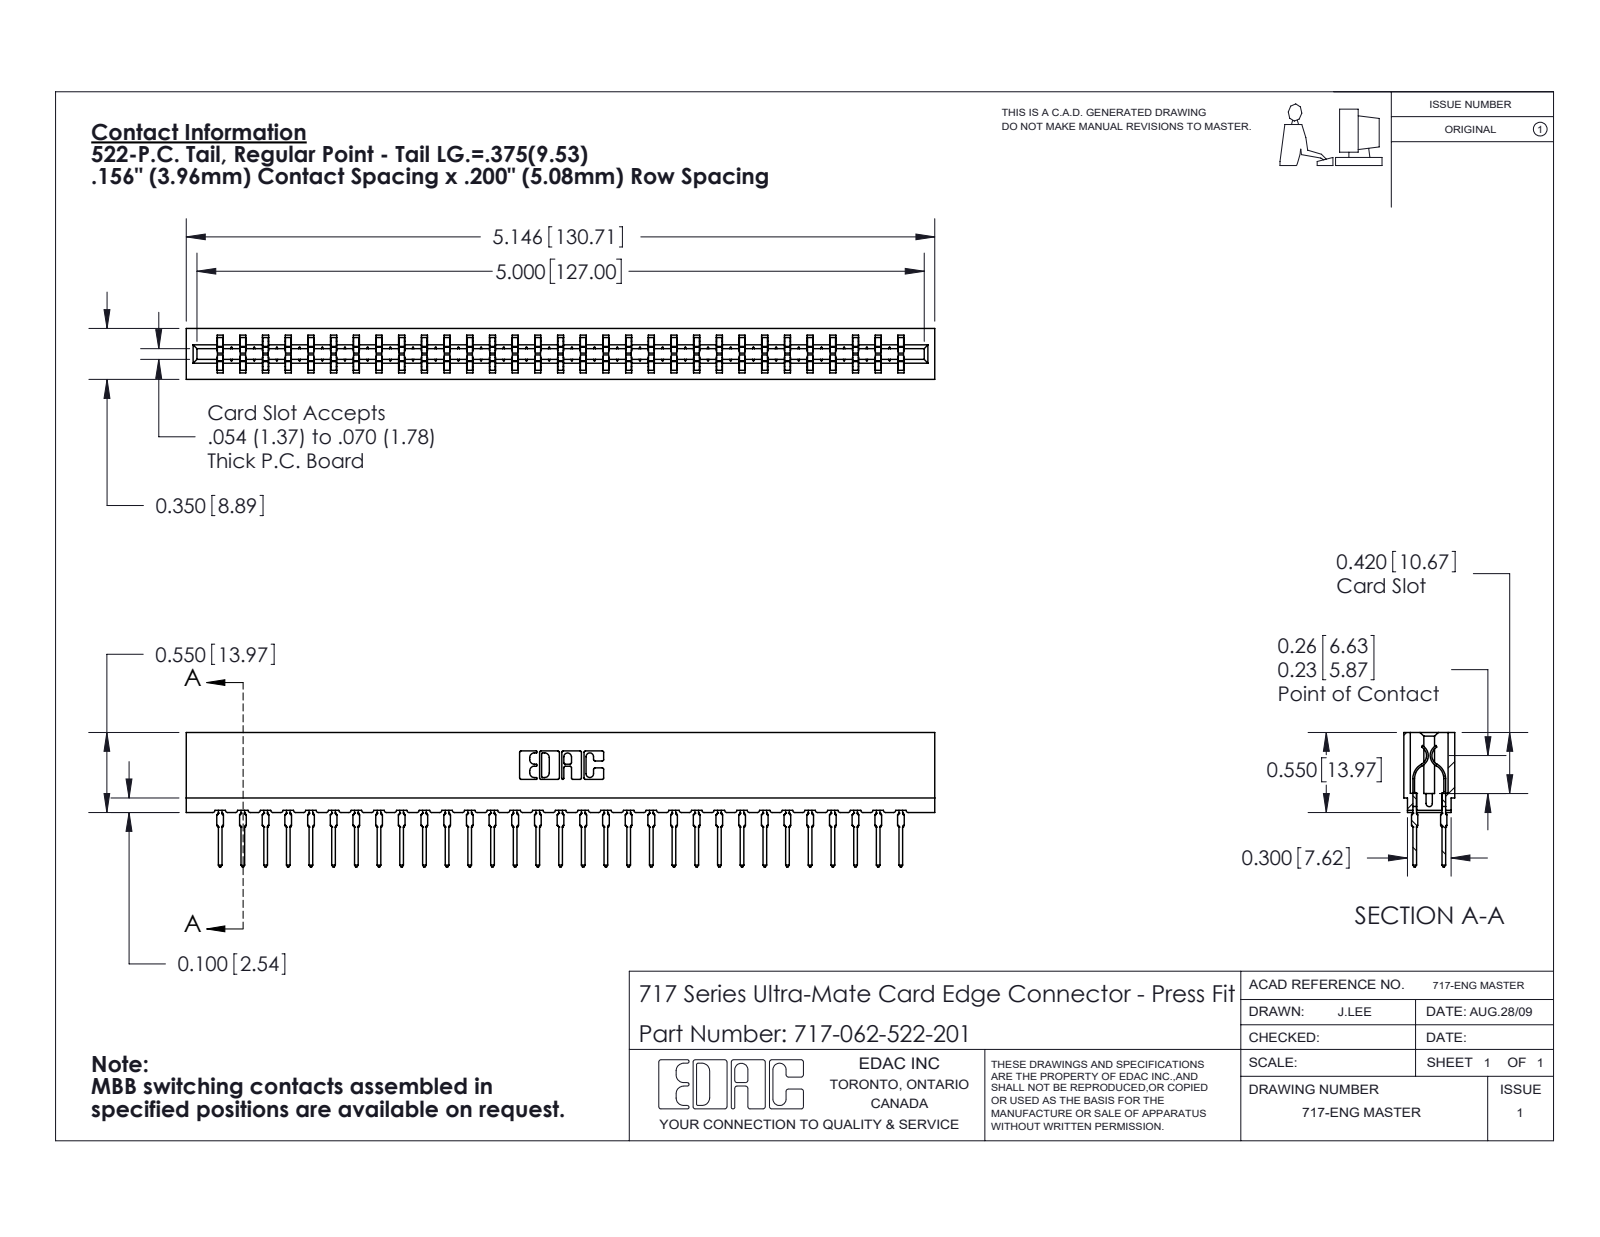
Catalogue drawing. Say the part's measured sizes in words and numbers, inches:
The part is named "745-292-001_522; 717 Part_Insulator Option - 06; 717-062-522-201". Its 3-D file was written by "SolidWorks 2020 (CONFIG_CONTROL_DESIGN)". It is 63 solids with 5674 faces: 2937 planar, 1125 cylindrical and 1612 other. Overall it measures 5.146 by 0.924 by 0.35 inches. Its volume is 0.698 cubic inches and its surface area 27.27 square inches. Partial cylindrical surfaces (rounded edges, fillets, slot ends): 124 of radius 0.021, 62 of radius 0.015, 22 of radius 0.01, 8 of radius 0.005, 8 of radius 0.011, 6 of radius 0.007, 6 of radius 0.031, 3 of radius 0.026. The main face-to-face distances are 0.212, 0.138, 0.35, 0.063, 0.287, 0.076, 0.149, 0.074, 0.045, 0.305.
